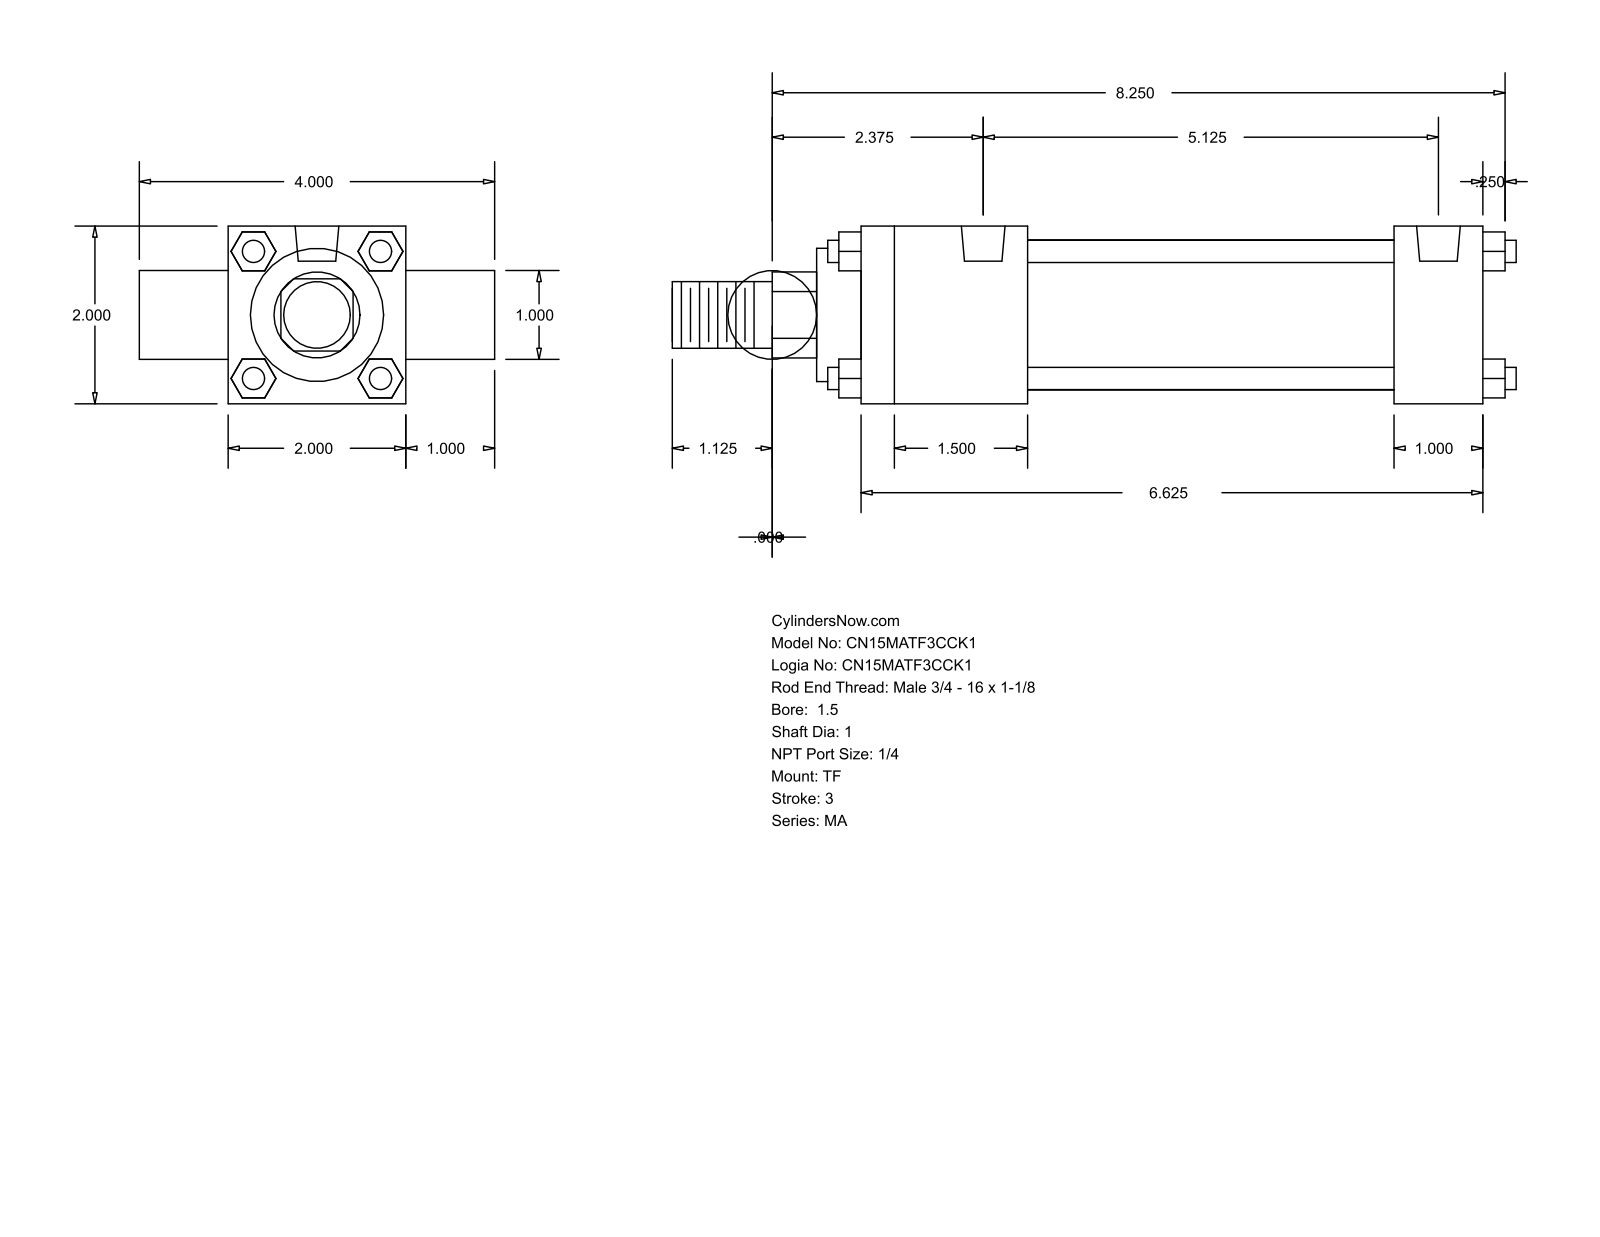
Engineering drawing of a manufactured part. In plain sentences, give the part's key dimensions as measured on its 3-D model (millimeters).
The part is named "MA_TF__0150_1". Its 3-D file was written by "GSSL Pune (CONFIG_CONTROL_DESIGN)". It is 0 solids with 120 faces: 92 planar, 28 cylindrical and 0 other. Overall it measures 241.3 by 101.6 by 50.8 millimeters. Round holes: 3 of diameter 7.94, 2 of diameter 12.49. Round bosses or shafts: 4 of diameter 6.35, 2 of diameter 25.4, 1 of diameter 42.93, 1 of diameter 38.1, 1 of diameter 19.05. Partial cylindrical surfaces (rounded edges, fillets, slot ends): 1 of radius 12.29. The main face-to-face distances are 50.8, 25.4, 177.8, 76.2, 6.35, 47.63, 152.4, 104.77, 130.17, 190.5. The hole center spacings are 130.17.
